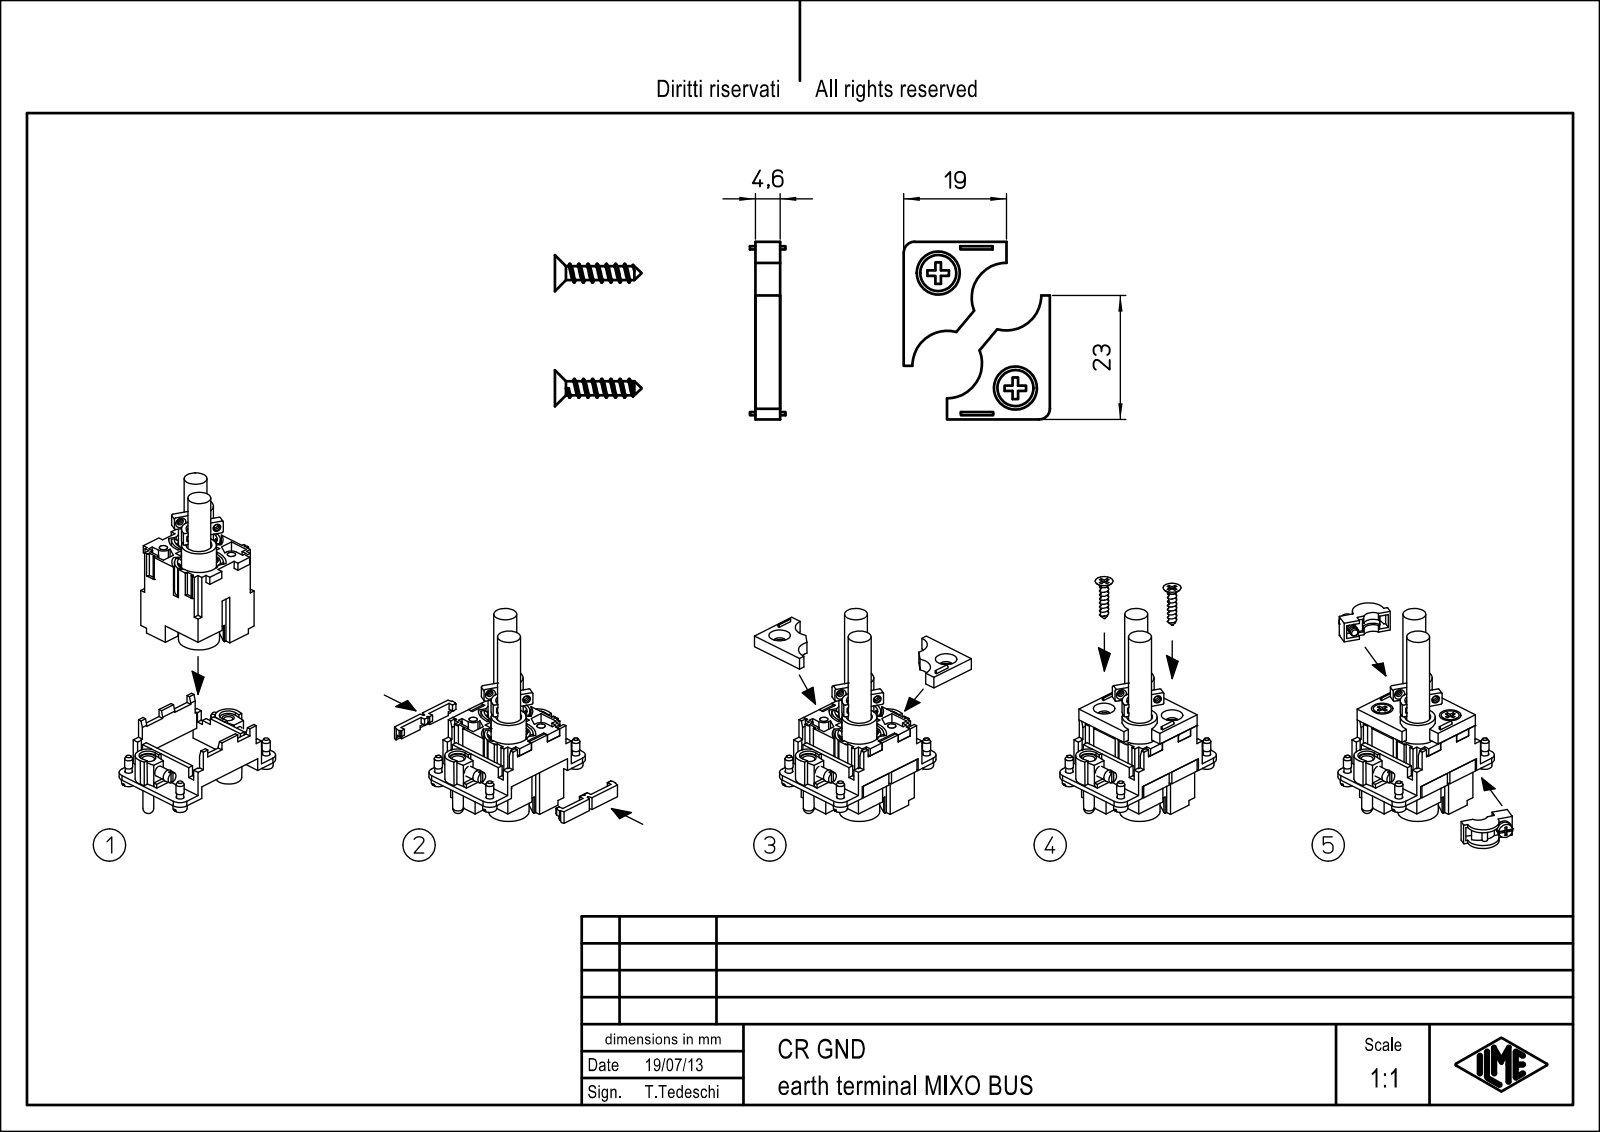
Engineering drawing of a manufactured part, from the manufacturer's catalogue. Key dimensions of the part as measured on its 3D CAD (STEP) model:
Part name (STEP PRODUCT): CR_GND_1; CR_GND_2; CR_GND
STEP written by: Creo Elements/Direct Modeling 18.0B 02-Dec-2011 (C) Parametric Technology GmbH (AUTOMOTIVE_DESIGN)
Units: millimetres
Bodies: 2 solids, 116 faces (66 planar, 40 cylindrical, 10 other)
Overall size (bounding box): 33.95 × 28.13 × 17
Volume: 2 722 mm³ · Surface area: 2 224 mm²
Round holes (diameter × count): ⌀6.8 ×2
Round bosses / shafts (diameter × count): ⌀6.7 ×2, ⌀2.6 ×2
Partial cylindrical surfaces — rounded edges, fillets, slot ends (radius × count): R6.5 ×4
Main face-to-face distances: 4.6, 28.13, 33.95, 1, 8.53, 19.6, 1.2, 1.9, 32.05, 32.75
Hole centre spacings: 25.71
